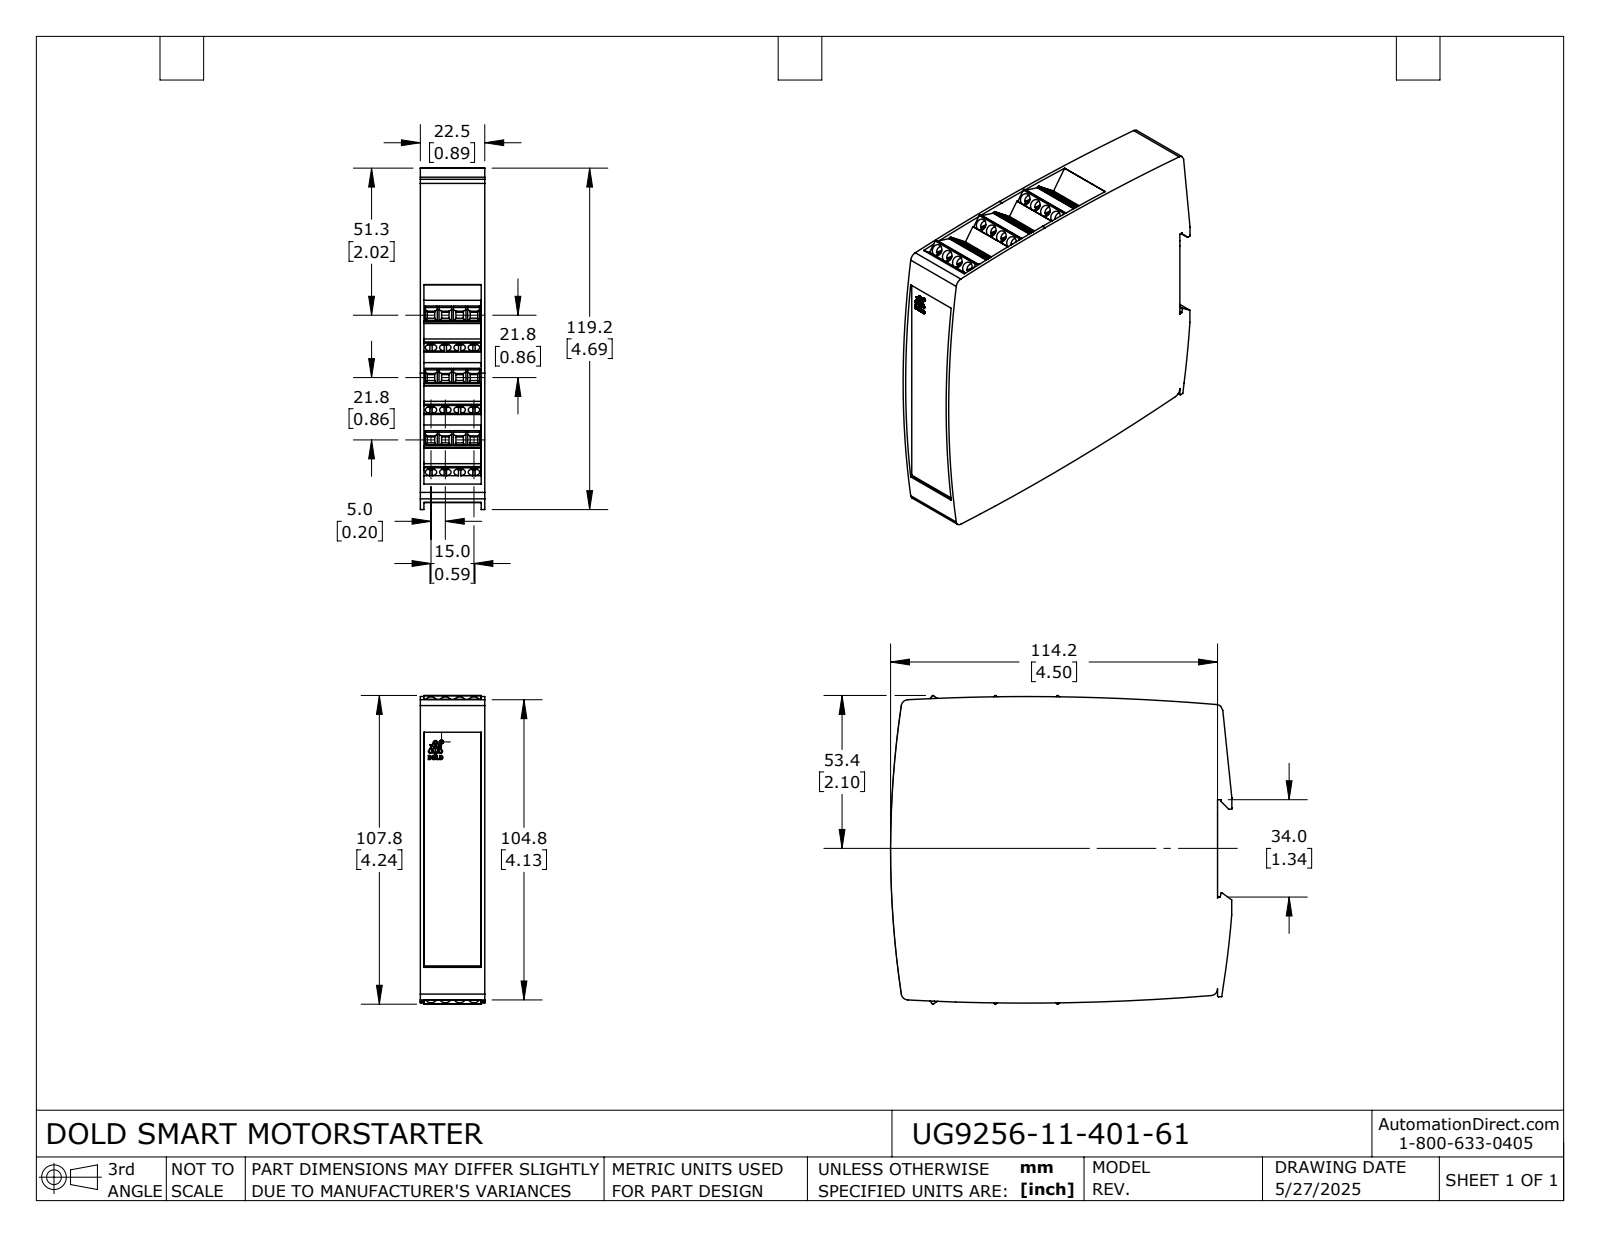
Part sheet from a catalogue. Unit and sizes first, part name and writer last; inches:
Units: inches
Overall size (bounding box): 4.693 × 4.243 × 0.886
Round holes (diameter × count): ⌀0.157 ×24, ⌀0.053 ×1
Round bosses / shafts (diameter × count): ⌀0.15 ×24, ⌀0.049 ×1
Partial cylindrical surfaces — rounded edges, fillets, slot ends (radius × count): R0.012 ×15, R0.02 ×14, R0.004 ×12, R0.094 ×7, R0.005 ×6, R0.004 ×4, R31.496 ×4, R0.021 ×3
Main face-to-face distances: 0.886, 0.049, 0.837, 0.675, 4.379, 0.051, 0.835, 1.35, 0.528, 0.785
Hole centre spacings: 0.563, 0.197, 0.528, 0.658, 0.394, 1.073, 0.792, 1.055
Volume: 15.85 in³ · Surface area: 64.72 in²
Bodies: 1 solid, 1036 faces (813 planar, 222 cylindrical, 1 other)
Part name (STEP PRODUCT): UG9256-11-401-61
STEP written by: SolidWorks 2024 (AUTOMOTIVE_DESIGN)
